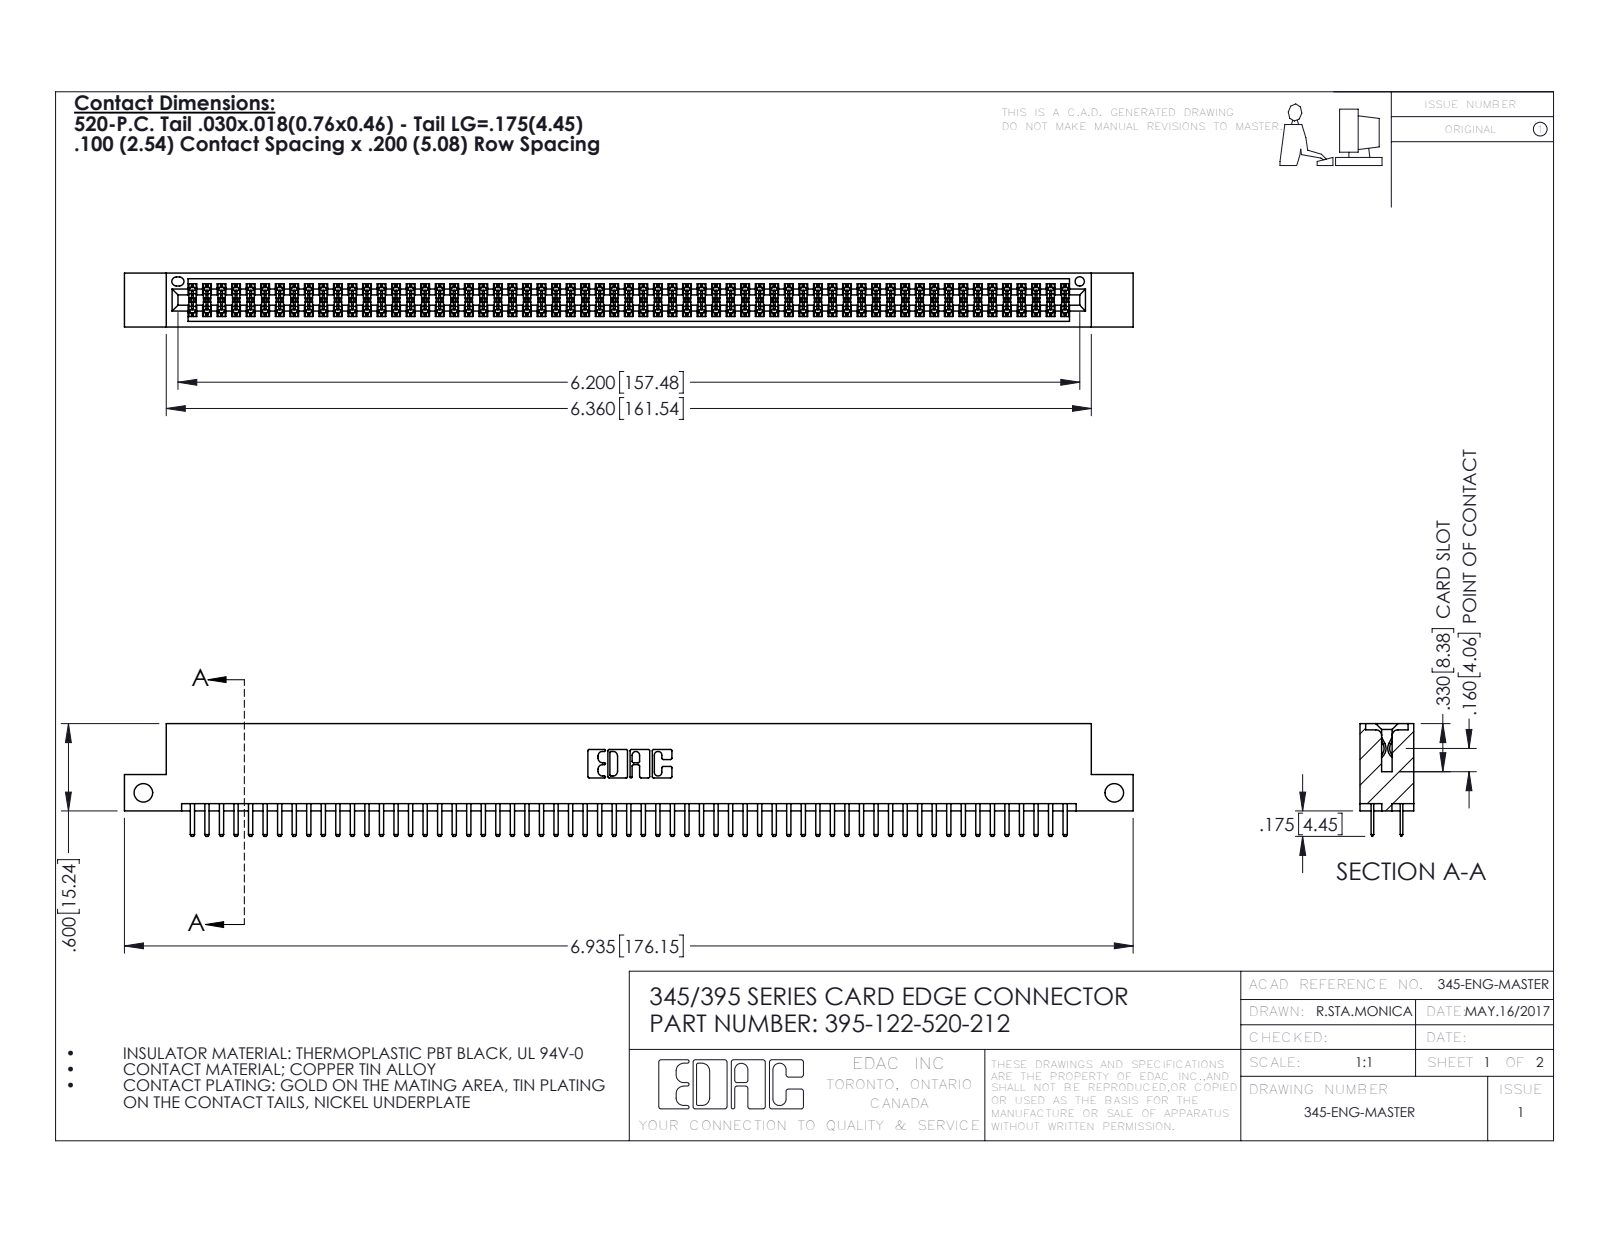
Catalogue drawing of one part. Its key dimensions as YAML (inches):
part_name: "345 Part_Flush Mounting Lugs - Side Mount; 395-122-520-212; 345-292-001_345-293-120"
step_written_by: "SolidWorks 2016 (CONFIG_CONTROL_DESIGN)"
units: inches
bodies: {solids: 123, faces: 6714, planar: 4350, cylindrical: 2364, other: 0}
overall_size: [6.935, 0.775, 0.37]
volume: 1.046
surface_area: 39.47
round_holes:
  - {diameter: 0.128, count: 2}
  - {diameter: 0.064, count: 1}
partial_cylinders:
  - {radius: 0.006, count: 183}
  - {radius: 0.01, count: 126}
  - {radius: 0.01, count: 22}
  - {radius: 0.007, count: 6}
  - {radius: 0.031, count: 6}
  - {radius: 0.026, count: 3}
  - {radius: 0.014, count: 2}
  - {radius: 0.019, count: 2}
face_to_face_distances: [0.298, 0.072, 0.2, 0.37, 0.098, 0.272, 0.025, 0.225, 0.022, 0.072]
hole_center_spacings: [6.675]
